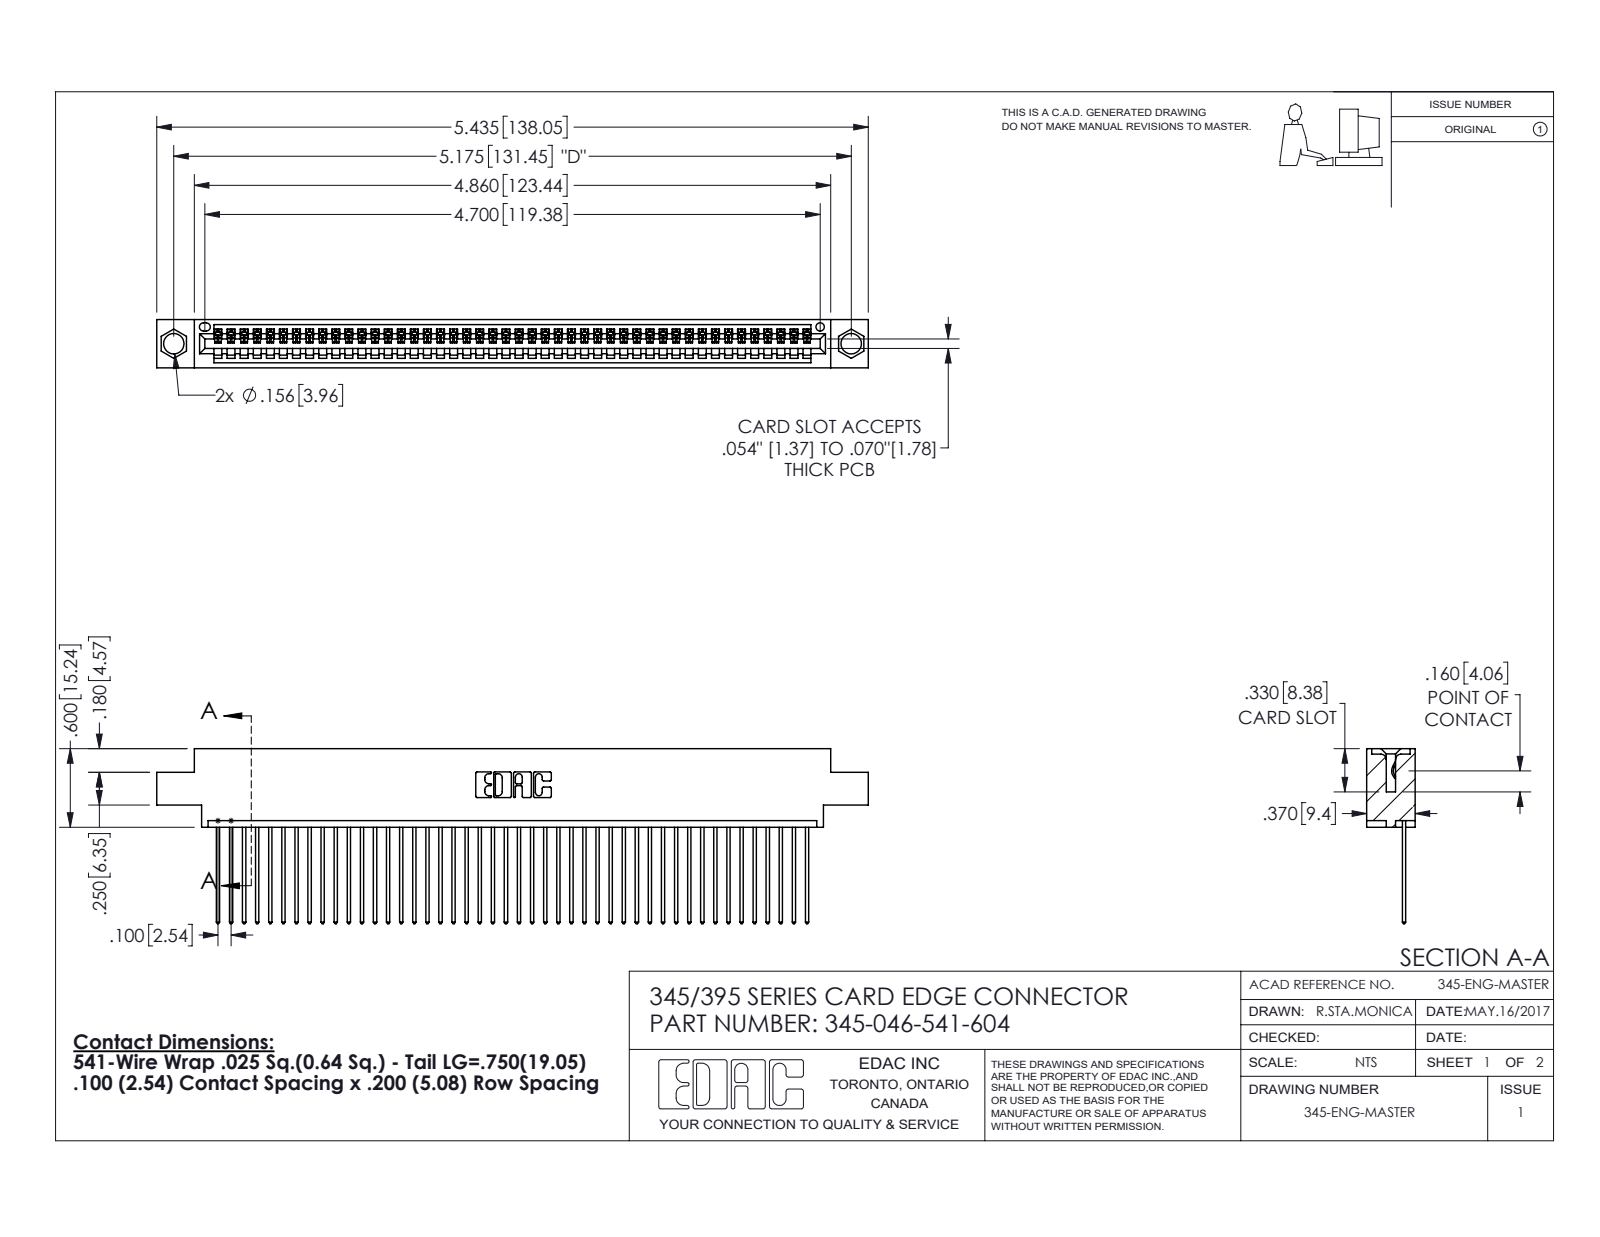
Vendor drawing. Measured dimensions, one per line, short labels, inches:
name: 345-292-001_345-293-141; 345 Part_0.170 Offset - 0.156 Dia-TH; 345-046-541-604
written by: SolidWorks 2016 (CONFIG_CONTROL_DESIGN)
unit: in
bodies: 47 solids, 2798 faces (1924 planar, 874 cylindrical, 0 other)
size: 5.435 × 1.337 × 0.37
volume: 0.799 in³; area: 28.34 in²
holes: 2× ⌀0.156, 1× ⌀0.064
rounds: 92× R0.006, 92× R0.01, 22× R0.01, 6× R0.007, 6× R0.031, 3× R0.026, 2× R0.031, 2× R0.04
face distances: 0.072, 0.298, 0.37, 0.098, 0.272, 0.025, 0.2, 0.225, 0.175, 0.149
hole spacings: 0.27, 4.939, 5.175
